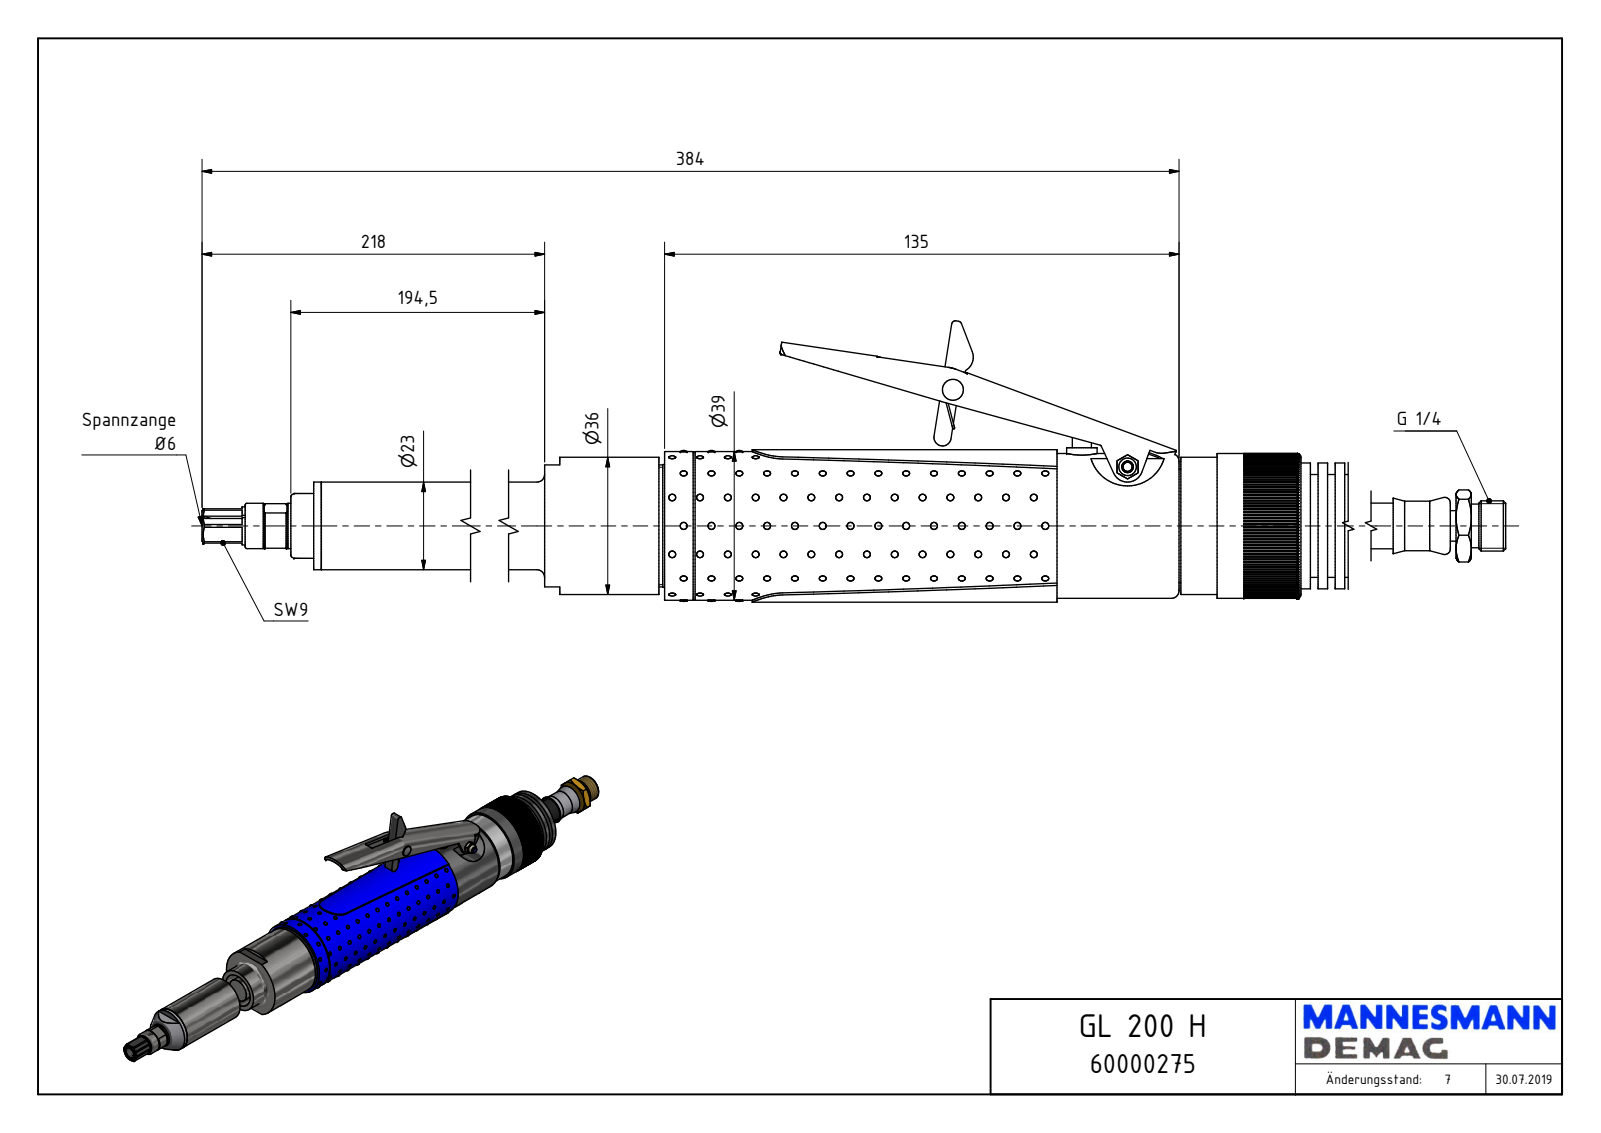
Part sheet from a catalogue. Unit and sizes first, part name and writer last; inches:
Units: inches
Overall size (bounding box): 15.327 × 2.951 × 1.559
Round holes (diameter × count): ⌀0.157 ×9, ⌀0.079 ×1, ⌀0.122 ×1, ⌀0.126 ×1, ⌀0.236 ×1, ⌀0.24 ×1, ⌀0.283 ×1, ⌀0.319 ×1, ⌀0.451 ×1, ⌀0.492 ×1, ⌀0.518 ×1, ⌀1.275 ×1
Round bosses / shafts (diameter × count): ⌀0.02 ×5, ⌀0.315 ×2, ⌀0.217 ×2, ⌀0.118 ×2, ⌀1.535 ×1, ⌀1.528 ×1, ⌀1.496 ×1, ⌀1.417 ×1
Partial cylindrical surfaces — rounded edges, fillets, slot ends (radius × count): R0.039 ×6, R0.138 ×4, R0.197 ×4, R0.787 ×4, R0.63 ×3, R0.02 ×2, R0.079 ×2, R0.118 ×2
Main face-to-face distances: 0.059, 0.197, 0.551, 6.555, 0.236, 0.177, 0.61, 1.24, 5.315, 0.433
Hole centre spacings: 0.472, 0.244, 0.668, 0.818, 0.913, 0.945, 1.972
Volume: 16.81 in³ · Surface area: 76.53 in²
Bodies: 1 solid, 480 faces (143 planar, 120 cylindrical, 217 other)
Part name (STEP PRODUCT): GL 200 H_60000275
STEP written by: Autodesk Inventor 2016 (AUTOMOTIVE_DESIGN)
